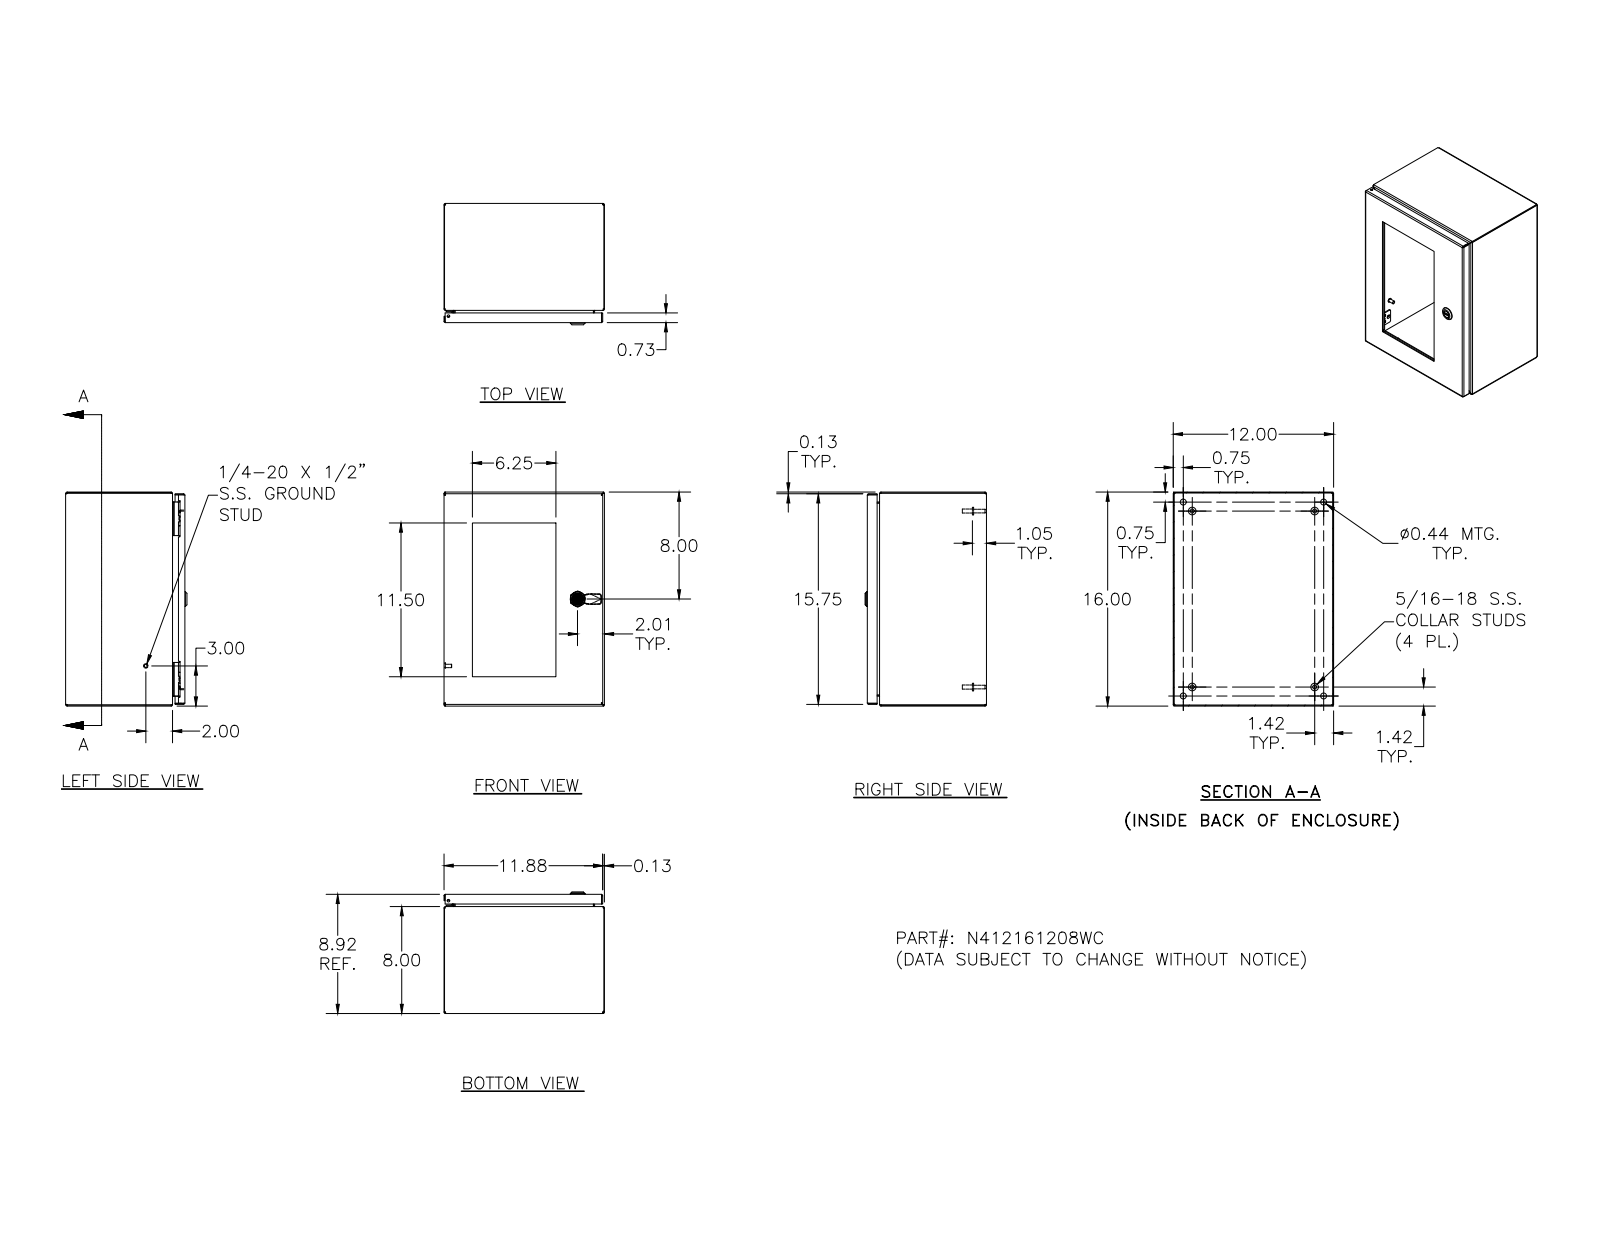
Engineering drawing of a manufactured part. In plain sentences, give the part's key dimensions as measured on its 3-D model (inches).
The part is named "N412161208WC". Its 3-D file was written by "SolidWorks 2018 (AUTOMOTIVE_DESIGN)". It is 57 solids with 1827 faces: 687 planar, 593 cylindrical and 547 other. Overall it measures 16 by 12 by 9.075 inches. Its volume is 91.16 cubic inches and its surface area 2 069 square inches. Round holes: 12 of diameter 0.156, 10 of diameter 0.281, 5 of diameter 0.188, 4 of diameter 0.093, 4 of diameter 0.152, 4 of diameter 0.167, 4 of diameter 0.172, 4 of diameter 0.437, 1 of diameter 0.187, 1 of diameter 0.197, 1 of diameter 0.315, 1 of diameter 0.394. Round bosses or shafts: 10 of diameter 0.337, 10 of diameter 0.25, 10 of diameter 0.19, 4 of diameter 0.563, 4 of diameter 0.36, 4 of diameter 0.32, 4 of diameter 0.3, 4 of diameter 0.275. Partial cylindrical surfaces (rounded edges, fillets, slot ends): 34 of radius 0.031, 30 of radius 0.012, 26 of radius 0.05, 24 of radius 0.105, 18 of radius 0.016, 16 of radius 0.125, 13 of radius 0.02, 8 of radius 0.032. The main face-to-face distances are 0.074, 8.843, 11.926, 15.926, 8.769, 12, 11.852, 8.917, 15.852, 16. The hole center spacings are 4, 12, 6.221, 8.5, 8.585, 11.862, 7.5, 0.5.
